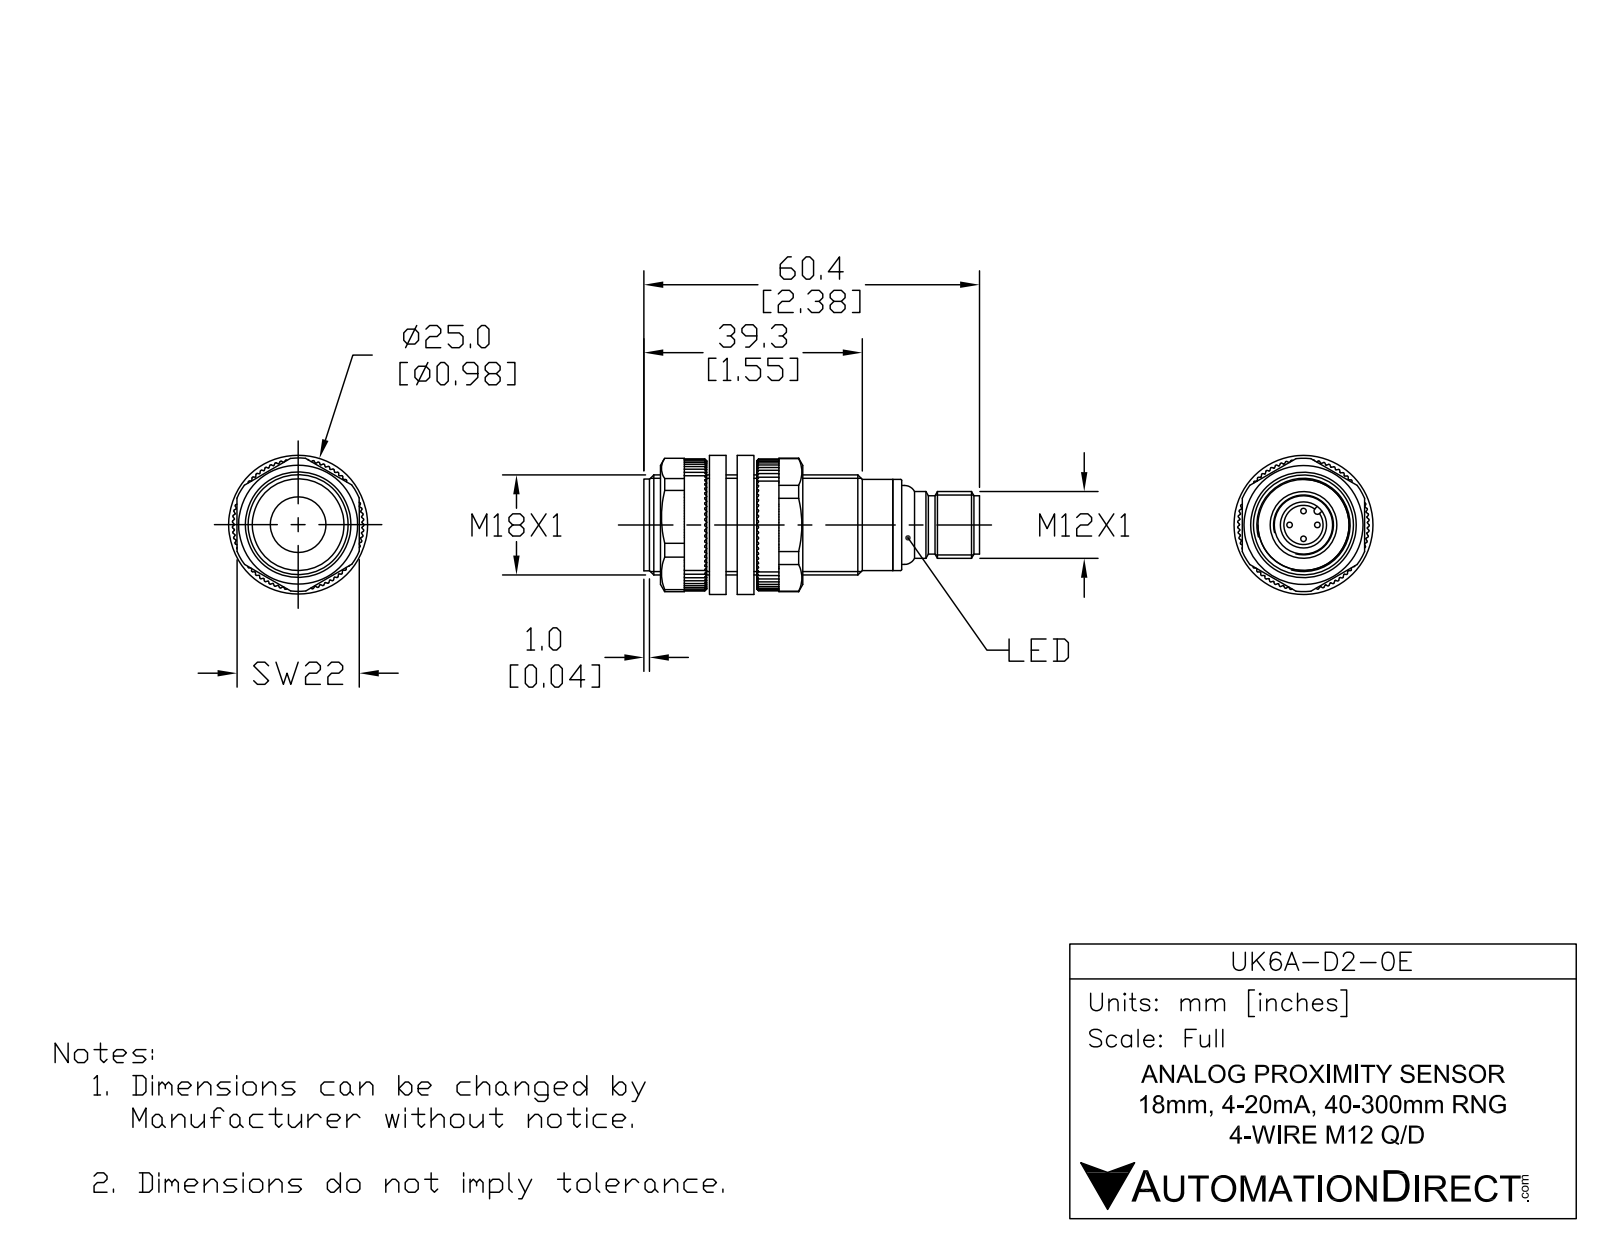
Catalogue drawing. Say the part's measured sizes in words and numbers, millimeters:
The part is named "UK6A-D2-0E". Its 3-D file was written by "SolidWorks 2017 (AUTOMOTIVE_DESIGN)". It is 4 solids with 86 faces: 15 planar, 36 cylindrical and 35 other. Overall it measures 60.3 by 18 by 18 millimeters. Its volume is 12 400 cubic millimeters and its surface area 4 934 square millimeters. Round holes: 1 of diameter 7, 1 of diameter 8.3, 1 of diameter 9.5. Round bosses or shafts: 4 of diameter 1, 1 of diameter 18, 1 of diameter 16.4, 1 of diameter 15.8, 1 of diameter 14.2, 1 of diameter 12, 1 of diameter 10.5. Partial cylindrical surfaces (rounded edges, fillets, slot ends): 1 of radius 0.6. The main face-to-face distances are 43.8, 1, 44.8, 1, 44.8, 46.3, 46.3, 45.3, 1.5, 51.4.
